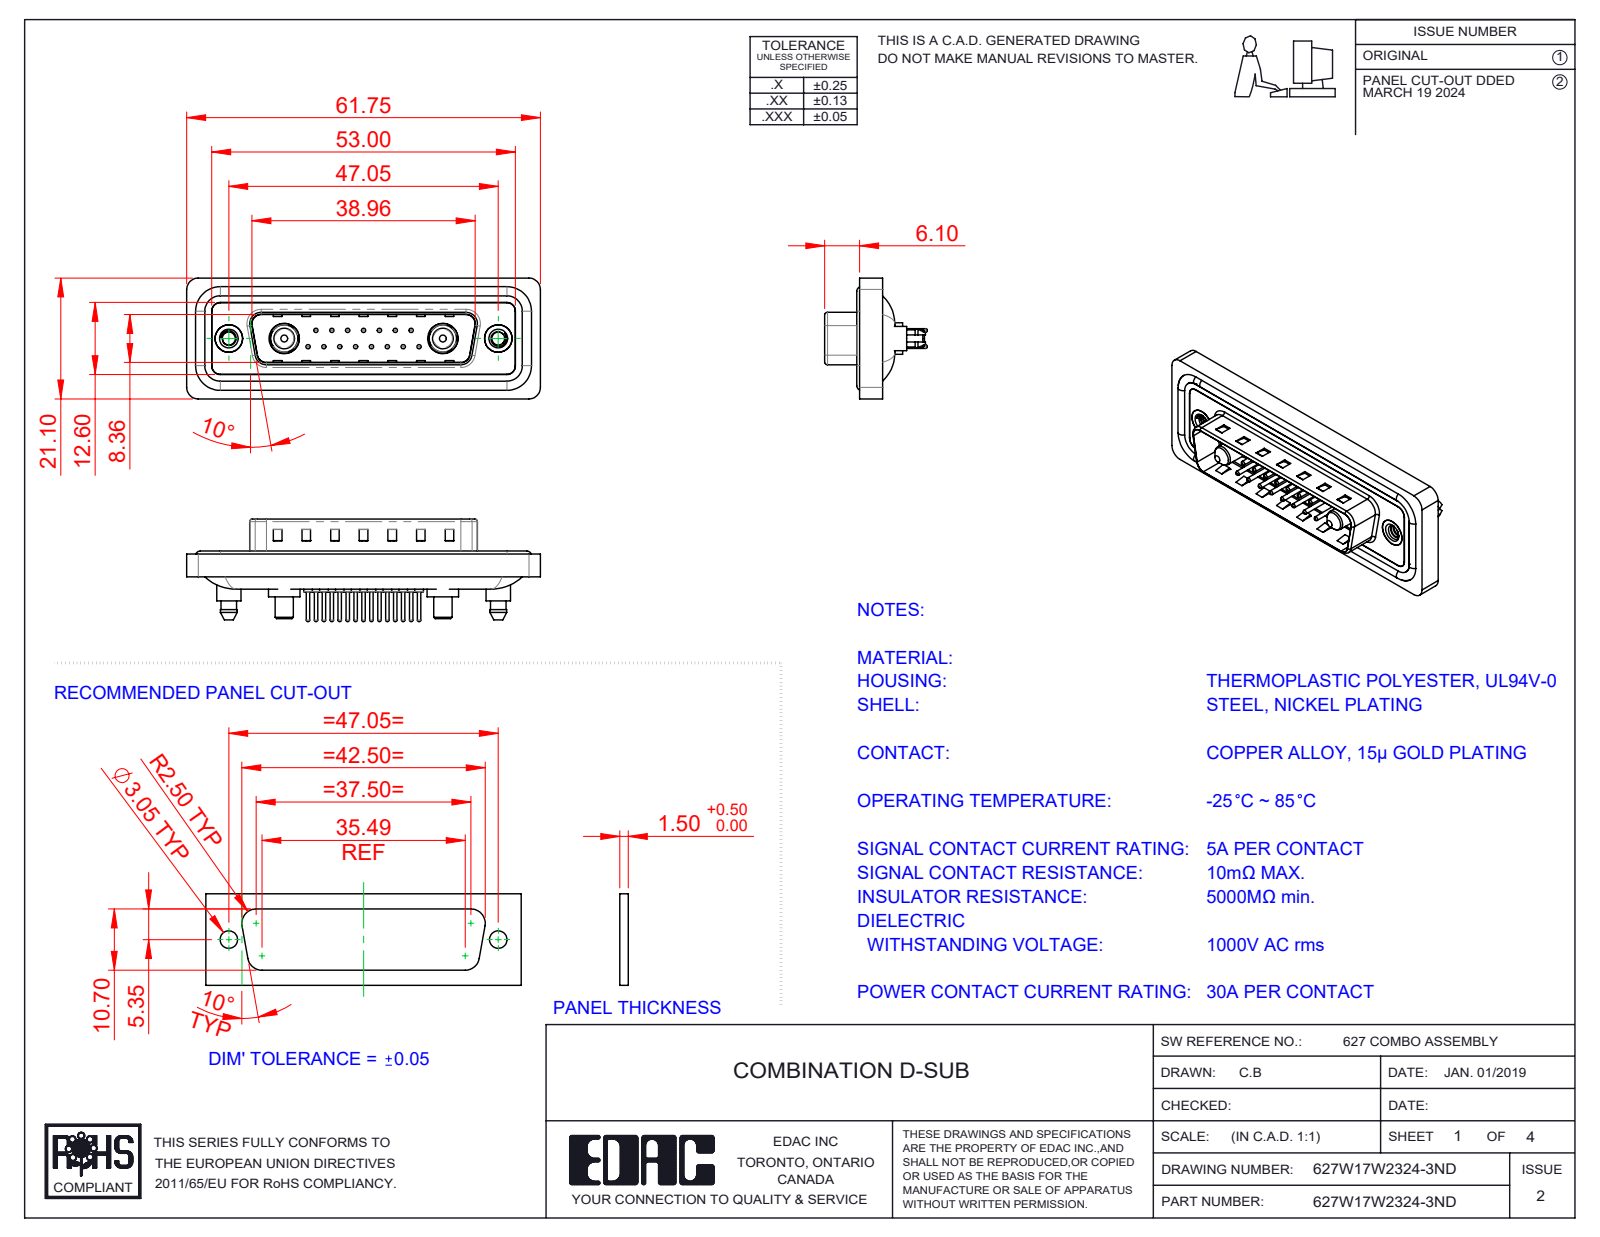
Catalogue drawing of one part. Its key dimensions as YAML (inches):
part_name: "627Combo Contact Row 1_24; 627W17W2324-3ND; 627Combo Threaded Boardlock_5; 627Combo Shell Rear_25 Contacts (+6 more)"
step_written_by: "SolidWorks 2023 (CONFIG_CONTROL_DESIGN)"
units: inches
bodies: {solids: 26, faces: 1174, planar: 350, cylindrical: 476, other: 348}
overall_size: [2.431, 0.831, 0.705]
volume: 0.452
surface_area: 19
round_holes:
  - {diameter: 0.03, count: 15}
  - {diameter: 0.063, count: 15}
  - {diameter: 0.079, count: 15}
  - {diameter: 0.089, count: 2}
  - {diameter: 0.157, count: 2}
  - {diameter: 0.189, count: 2}
  - {diameter: 0.191, count: 2}
  - {diameter: 0.197, count: 2}
  - {diameter: 0.209, count: 2}
round_bosses_or_shafts:
  - {diameter: 0.059, count: 15}
  - {diameter: 0.024, count: 15}
  - {diameter: 0.063, count: 4}
  - {diameter: 0.217, count: 2}
  - {diameter: 0.213, count: 2}
  - {diameter: 0.205, count: 2}
  - {diameter: 0.193, count: 2}
  - {diameter: 0.187, count: 2}
partial_cylinders:
  - {radius: 0.059, count: 24}
  - {radius: 0.079, count: 18}
  - {radius: 0.063, count: 10}
  - {radius: 0.02, count: 8}
  - {radius: 0.01, count: 4}
  - {radius: 0.024, count: 4}
  - {radius: 0.026, count: 4}
  - {radius: 0.035, count: 4}
face_to_face_distances: [0.016, 0.059, 0.043, 0.063, 0.02, 0.122, 0.114, 0.032, 0.377, 0.161]
hole_center_spacings: [0.124, 0.109, 0.218, 0.327, 0.198, 0.295, 0.436, 0.198]
